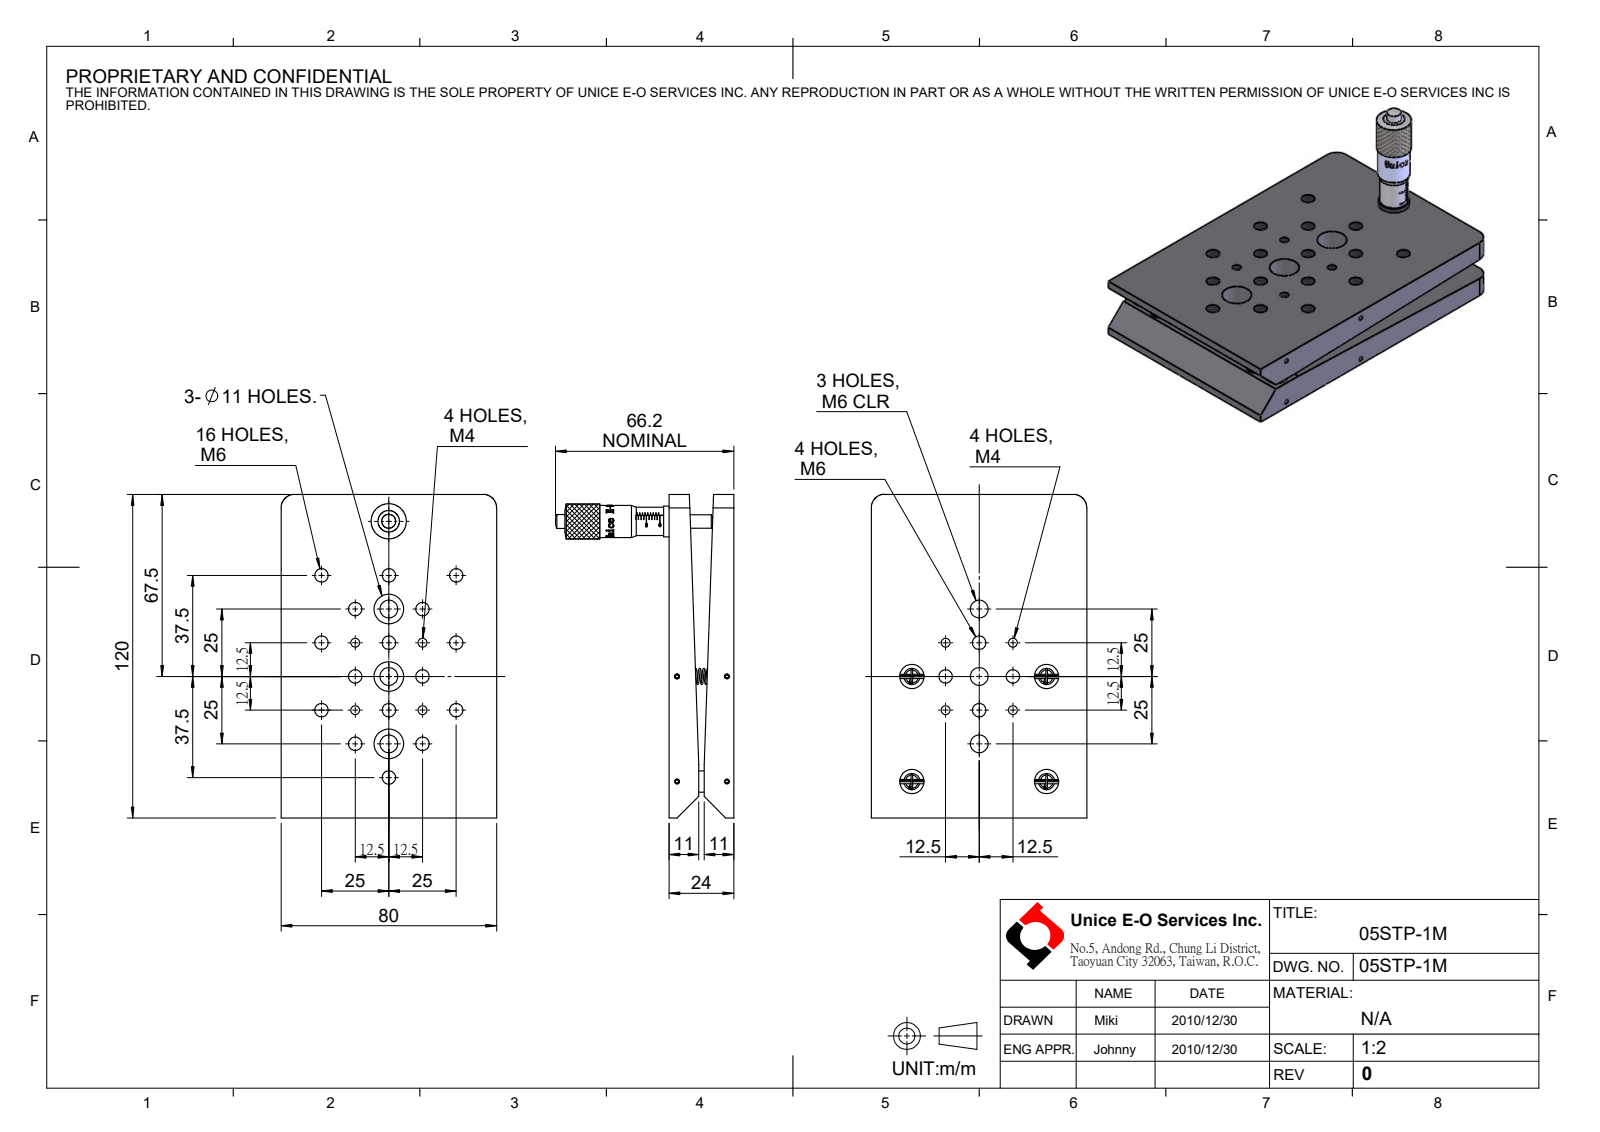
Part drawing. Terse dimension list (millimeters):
name: 05STP-1M
written by: SolidWorks 2016 (CONFIG_CONTROL_DESIGN)
unit: mm
bodies: 21 solids, 694 faces (305 planar, 197 cylindrical, 192 other)
size: 120 × 80 × 66.2
volume: 168 079 mm³; area: 59 091 mm²
holes: 17× ⌀5, 5× ⌀3.3, 4× ⌀1.2, 4× ⌀1.8, 4× ⌀9, 3× ⌀6.6, 3× ⌀11, 1× ⌀9.5, 1× ⌀9.6, 1× ⌀10.6
bosses: 4× ⌀1.6, 4× ⌀0.6, 1× ⌀13, 1× ⌀12, 1× ⌀11.5, 1× ⌀10.5, 1× ⌀9.9, 1× ⌀9.2
rounds: 2× R5, 1× R5.98
face distances: 24, 80, 13, 11, 2, 120, 1, 12, 10, 23
hole spacings: 27.95, 12.5, 17.68, 39.53, 25, 45.07, 35.36, 37.5
